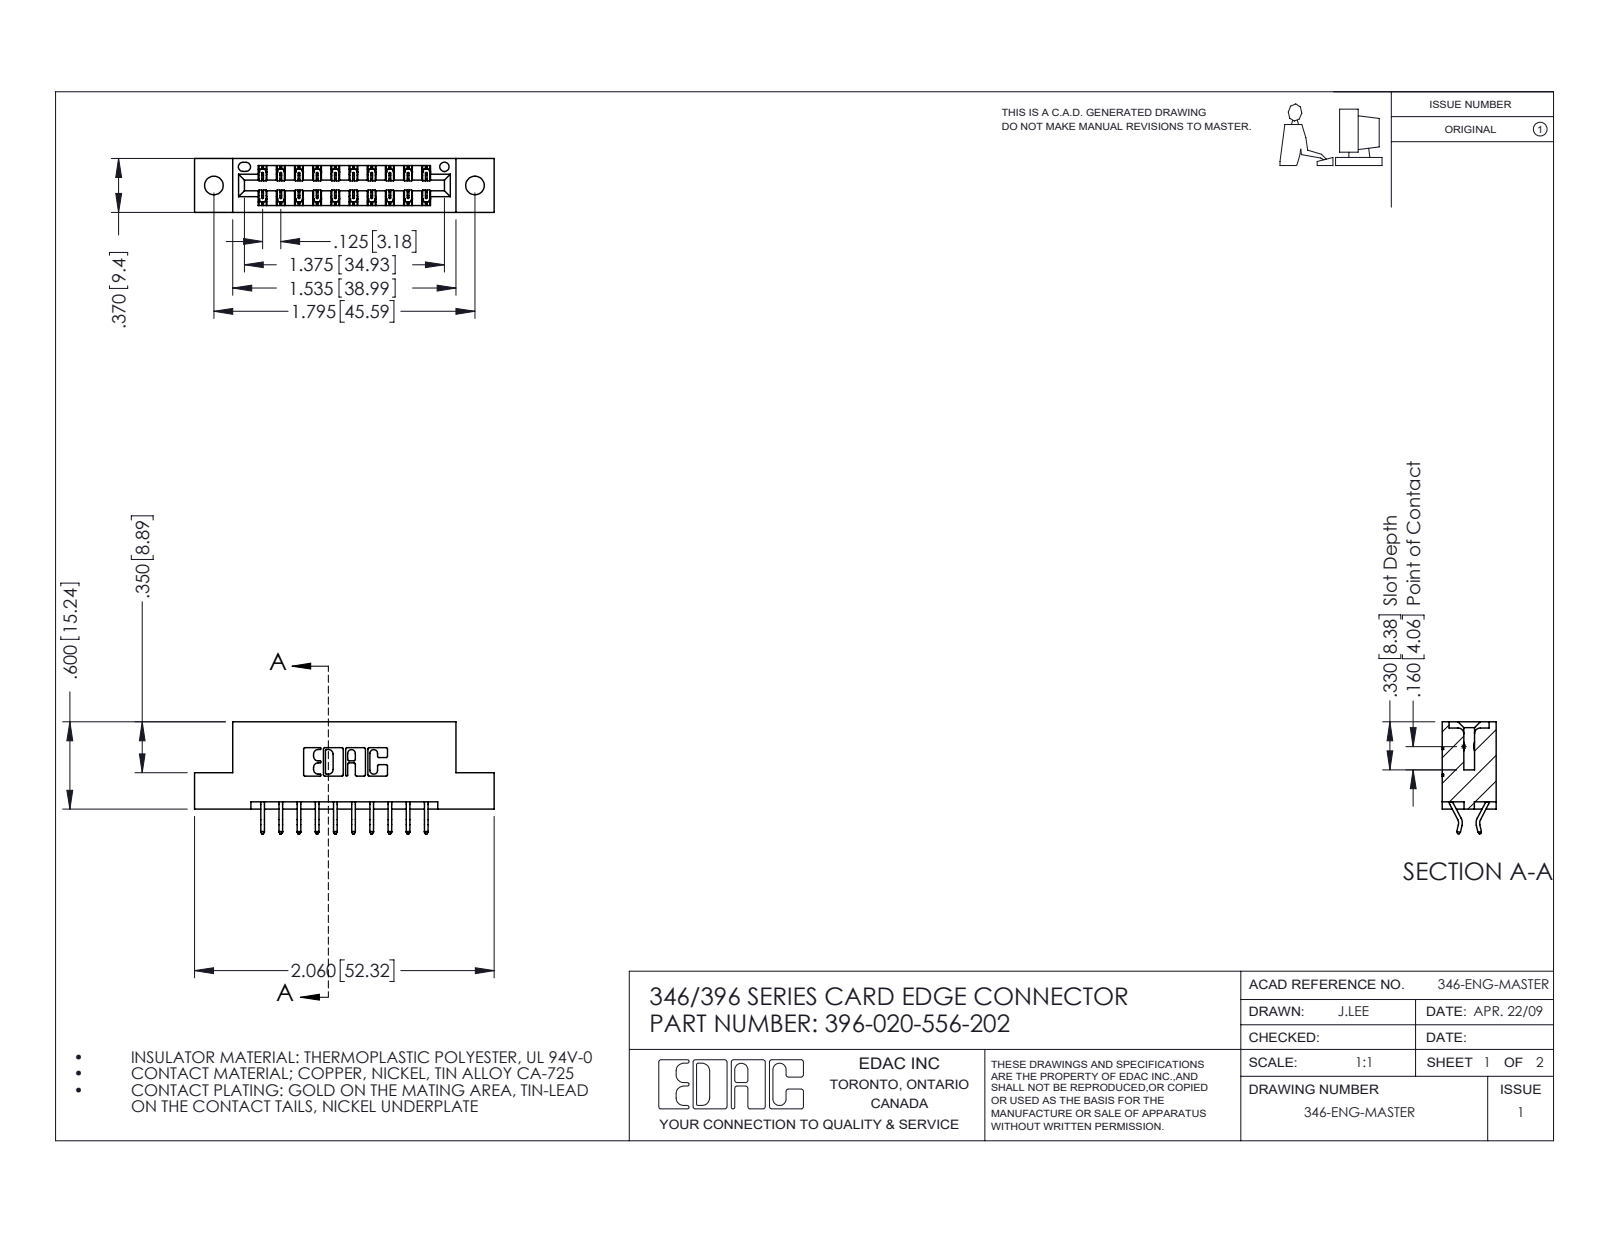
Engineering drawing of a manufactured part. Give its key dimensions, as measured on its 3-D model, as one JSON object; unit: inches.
{"part_name": "346 Part_Flush Mounting Lugs - 0.128 Dia; 396-020-556-202; 345-292-001_556 Tail", "step_written_by": "SolidWorks 2016 (CONFIG_CONTROL_DESIGN)", "units": "inches", "bodies": {"solids": 21, "faces": 1282, "planar": 856, "cylindrical": 426, "other": 0}, "overall_size": [2.06, 0.77, 0.37], "volume_in3": 0.294, "surface_area_in2": 9.036, "round_holes": [[0.128, 2], [0.064, 1]], "partial_cylinders_radius": [[0.006, 30], [0.01, 22], [0.007, 6], [0.031, 6], [0.026, 3], [0.01, 2], [0.014, 2], [0.022, 2]], "face_to_face_distances": [0.25, 0.048, 0.322, 0.37, 0.025, 0.072, 0.298, 0.148, 0.222, 0.1], "hole_center_spacings": [0.246, 1.59, 1.795]}
